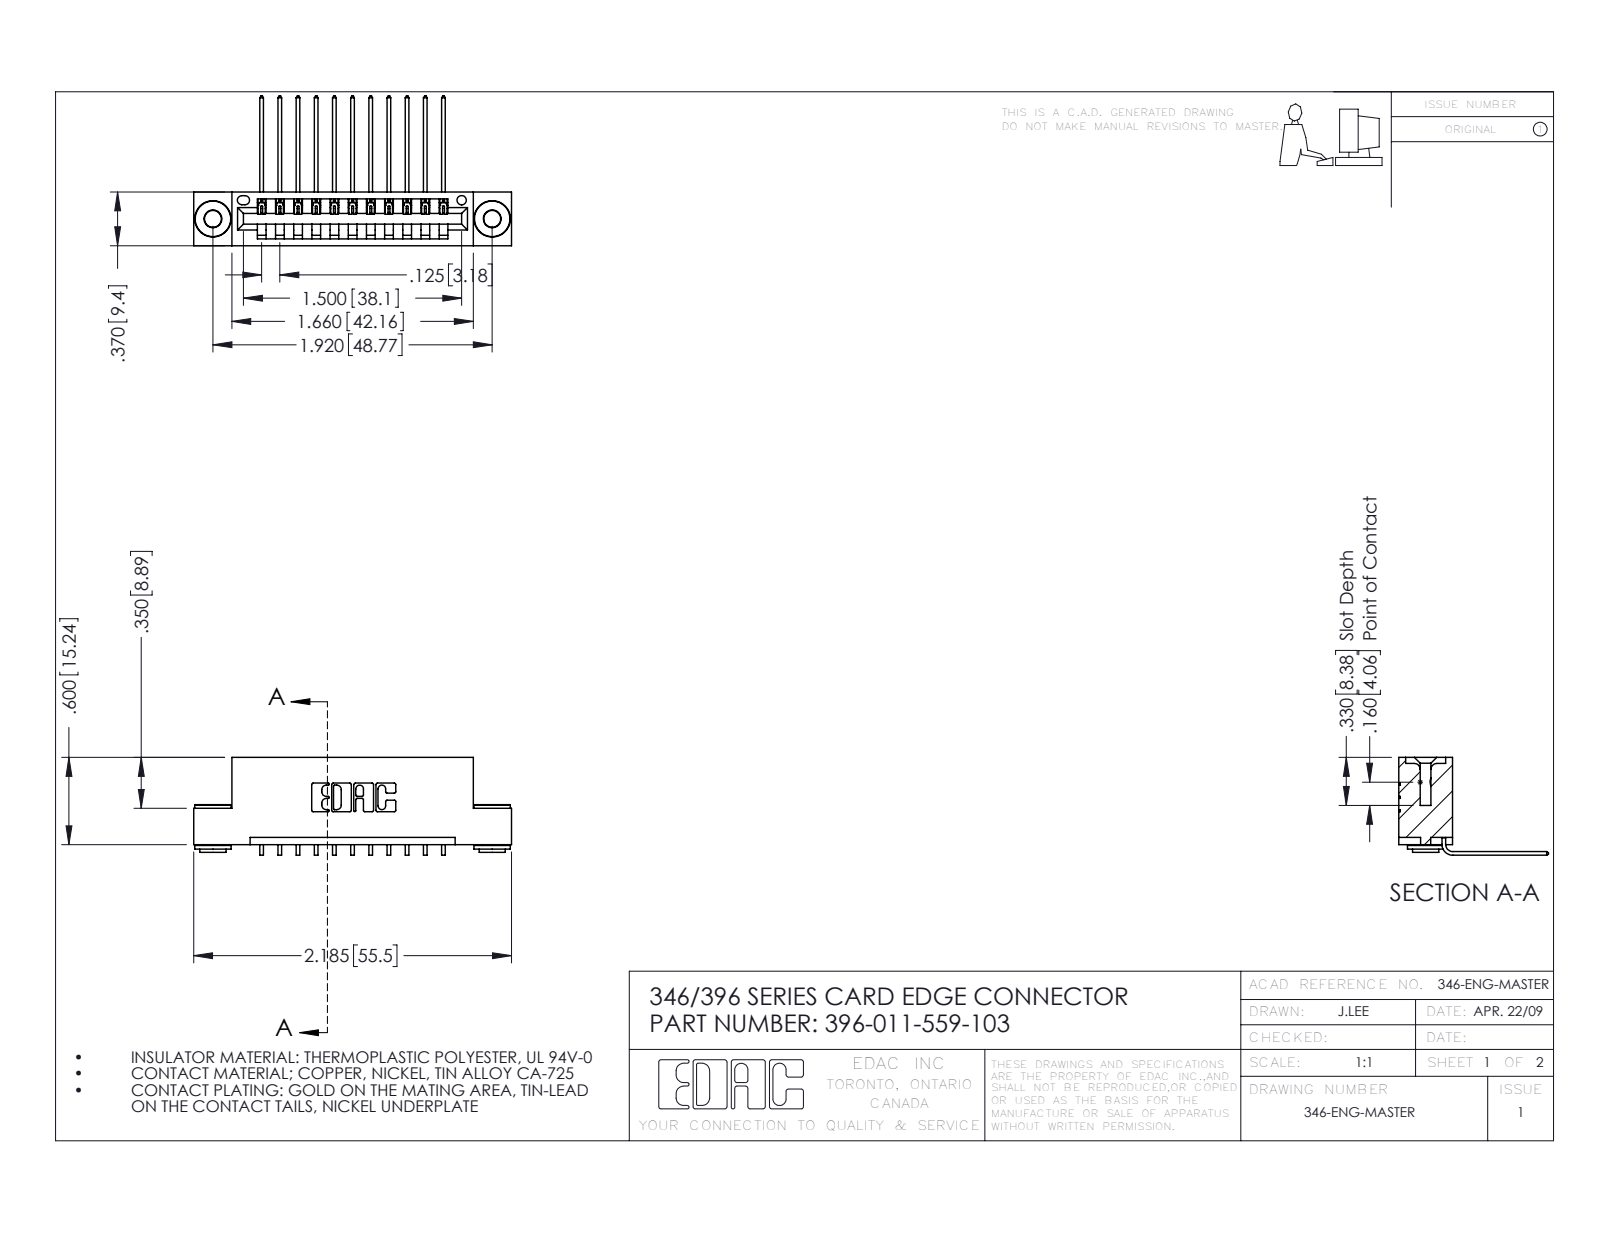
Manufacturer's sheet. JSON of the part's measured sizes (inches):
{"part_name": "345-292-001_558 559 Tail - 1; 396-011-559-103; 346 Part_Flush Mounting Lugs - 0.156 Dia-TH; 345-250-002_345-250-002-102", "step_written_by": "SolidWorks 2016 (CONFIG_CONTROL_DESIGN)", "units": "inches", "bodies": {"solids": 14, "faces": 820, "planar": 548, "cylindrical": 264, "other": 8}, "overall_size": [2.185, 1.03, 0.673], "volume_in3": 0.315, "surface_area_in2": 10.15, "round_holes": [[0.116, 2], [0.156, 2], [0.064, 1]], "round_bosses_or_shafts": [[0.25, 2], [0.18, 2], [0.136, 2]], "partial_cylinders_radius": [[0.006, 22], [0.01, 22], [0.007, 6], [0.031, 6], [0.026, 3], [0.031, 2], [0.04, 2], [0.014, 1]], "face_to_face_distances": [0.25, 0.048, 0.322, 0.37, 0.025, 0.072, 0.298, 0.148, 0.222, 0.1], "hole_center_spacings": [0.246, 1.715, 1.92]}
